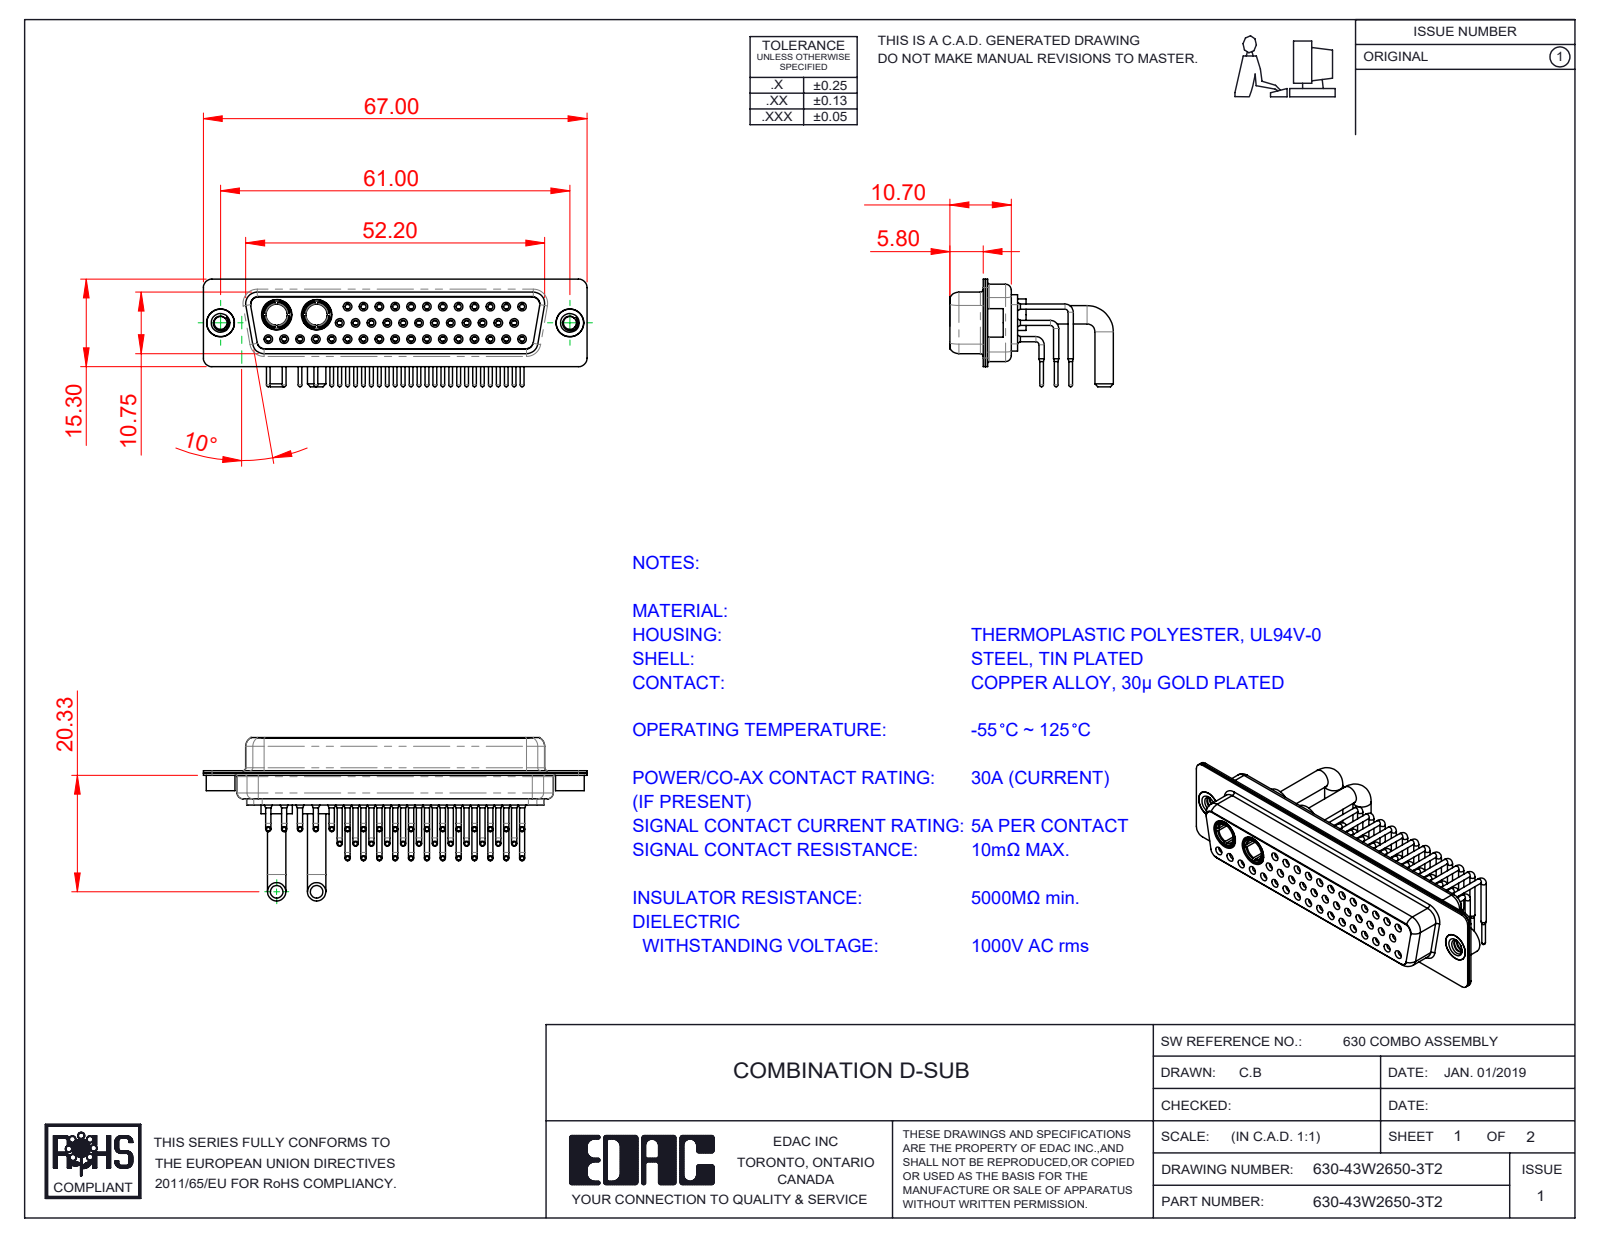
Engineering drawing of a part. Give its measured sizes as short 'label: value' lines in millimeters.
name: Power Socket_Ext 30A RA 50; 630Combo Contact Row 2_50 Contacts; 630Combo Contact Row 1_50 Contacts; 630Combo Threaded Rivet_2 (+5 more)
written by: SolidWorks 2020 (CONFIG_CONTROL_DESIGN)
unit: mm
bodies: 50 solids, 2608 faces (740 planar, 1130 cylindrical, 738 other)
size: 67 × 28.53 × 18.8
volume: 7 426 mm³; area: 16 072 mm²
holes: 41× ⌀0.9, 41× ⌀1.1, 41× ⌀1.5, 41× ⌀2, 29× ⌀1.6, 12× ⌀1.7, 4× ⌀4.85, 2× ⌀2.26, 2× ⌀3.7, 2× ⌀4, 2× ⌀4.05, 2× ⌀5.3
bosses: 41× ⌀0.9, 41× ⌀0.65, 12× ⌀1.6, 4× ⌀3.2, 2× ⌀5.5, 2× ⌀5.2, 2× ⌀5, 2× ⌀4.96
rounds: 16× R1.5, 12× R1.35, 12× R2, 8× R1.6, 4× R0.25, 4× R0.5, 4× R0.6, 4× R0.65
face distances: 0.4, 6, 5.6, 0.8, 11.28, 1.82, 5.8, 10.35, 11.8, 6.2
hole spacings: 2.77, 3.16, 5.54, 8.31, 11.08, 13.85, 16.62, 19.39
